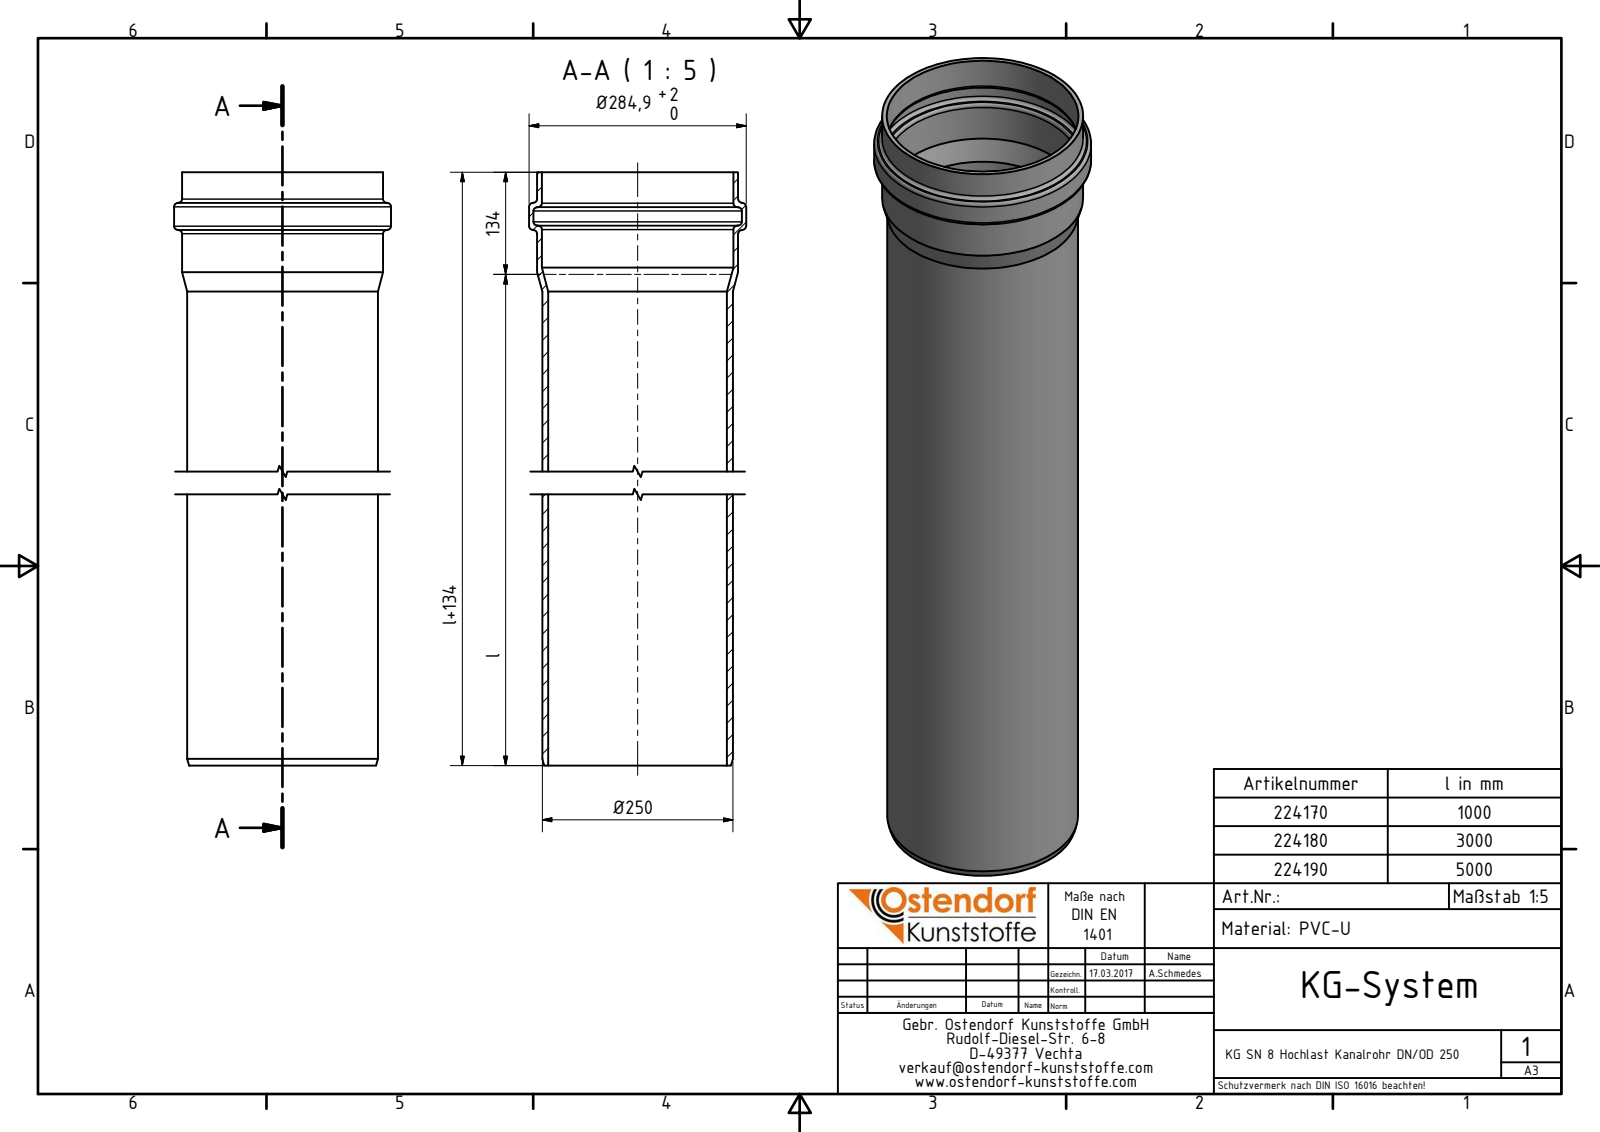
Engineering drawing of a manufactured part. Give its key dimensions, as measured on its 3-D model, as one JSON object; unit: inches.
{"part_name": "224180 KGEM Passlängen SN 8 DN_OD 250x3000", "step_written_by": "Autodesk Inventor 2016 (AUTOMOTIVE_DESIGN)", "units": "inches", "bodies": {"solids": 1, "faces": 25, "planar": 2, "cylindrical": 8, "other": 15}, "overall_size": [123.386, 11.217, 11.217], "volume_in3": 1135, "surface_area_in2": 7477, "round_holes": [[9.238, 1], [9.902, 1], [10.783, 1]], "round_bosses_or_shafts": [[11.217, 1], [10.39, 1], [9.852, 1]], "face_to_face_distances": [123.386]}
